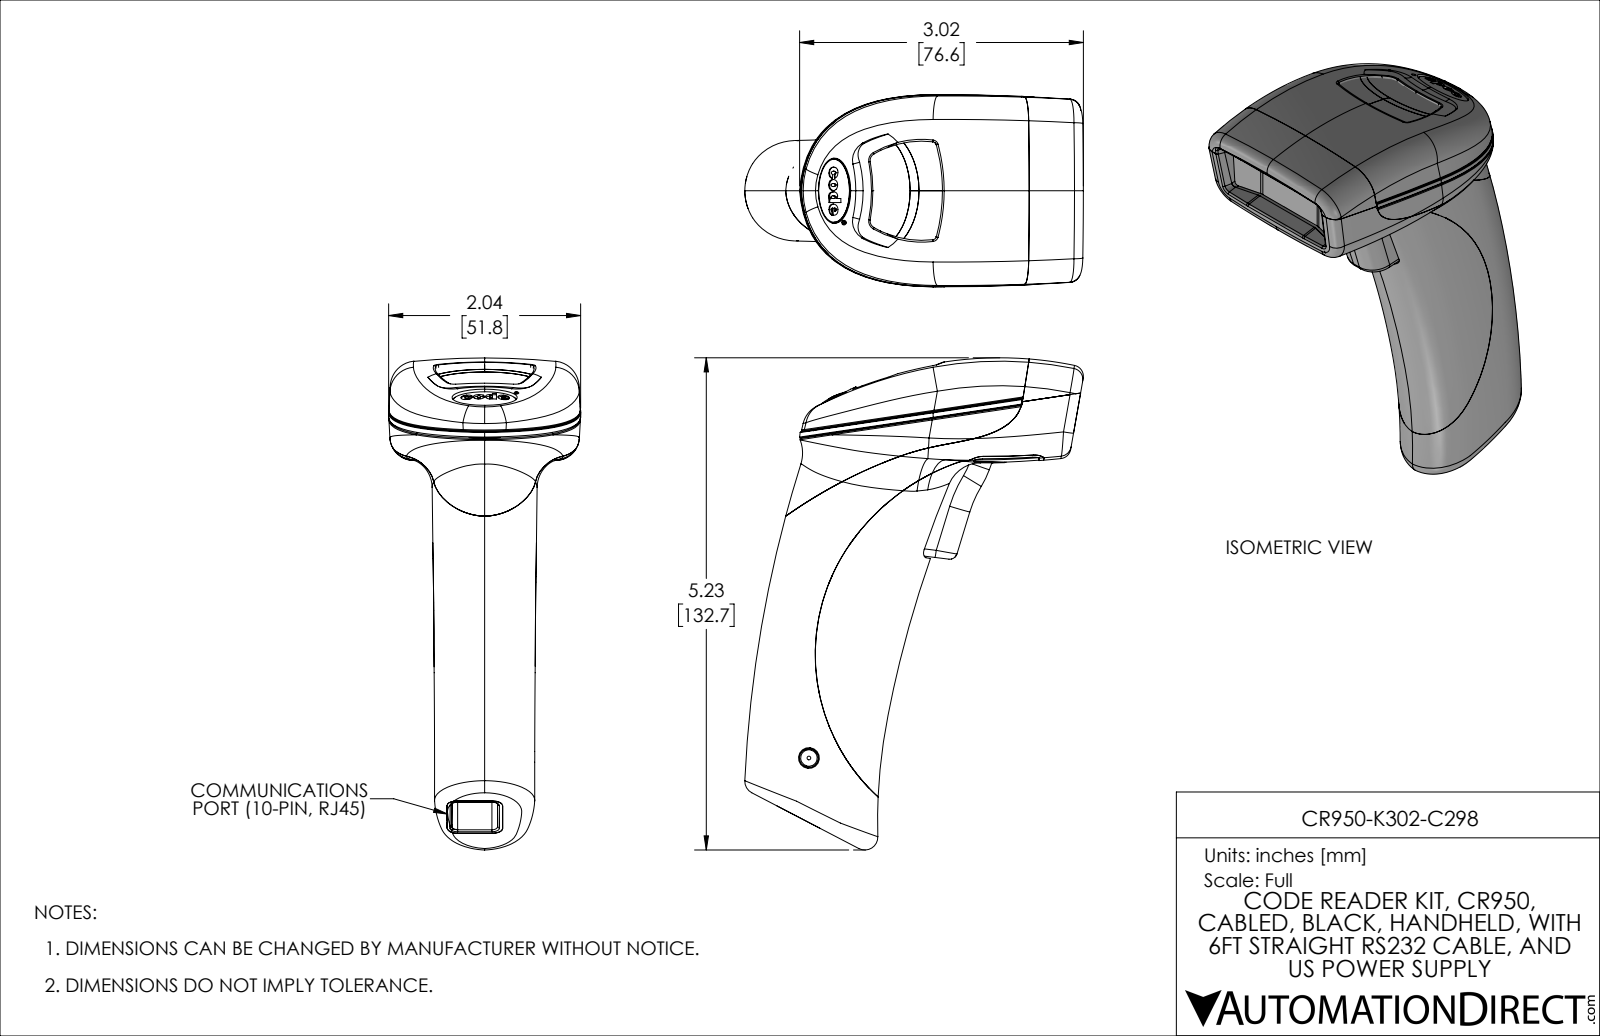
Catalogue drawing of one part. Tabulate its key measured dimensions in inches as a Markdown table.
| quantity | value |
| --- | --- |
| part name | CR950_NEW_2 |
| STEP written by | SolidWorks 2019 (AUTOMOTIVE_DESIGN) |
| units | inches |
| bodies | 4 solids, 2158 faces (947 planar, 316 cylindrical, 895 other) |
| overall size | 5.226 × 3.598 × 2.041 |
| volume | 4.573 in³ |
| surface area | 98.03 in² |
| round holes (diameter × count) | 0.039 × 6 |
| round bosses / shafts (diameter × count) | 0.018 × 20, 0.118 × 1 |
| partial cylindrical surfaces (radius × count) | 0.02 × 80, 0.039 × 21, 0.118 × 12, 0.008 × 10, 0.079 × 9, 0.03 × 8, 0.01 × 6, 0.02 × 5 |
| main face-to-face distances | 0.102, 0.087, 0.039, 0.047, 0.126, 0.126, 0.093, 0.5, 1.339, 1.102 |
| hole center spacings | 0.335, 1.063, 0.669, 0.728, 1.398, 0.394, 1.732 |
